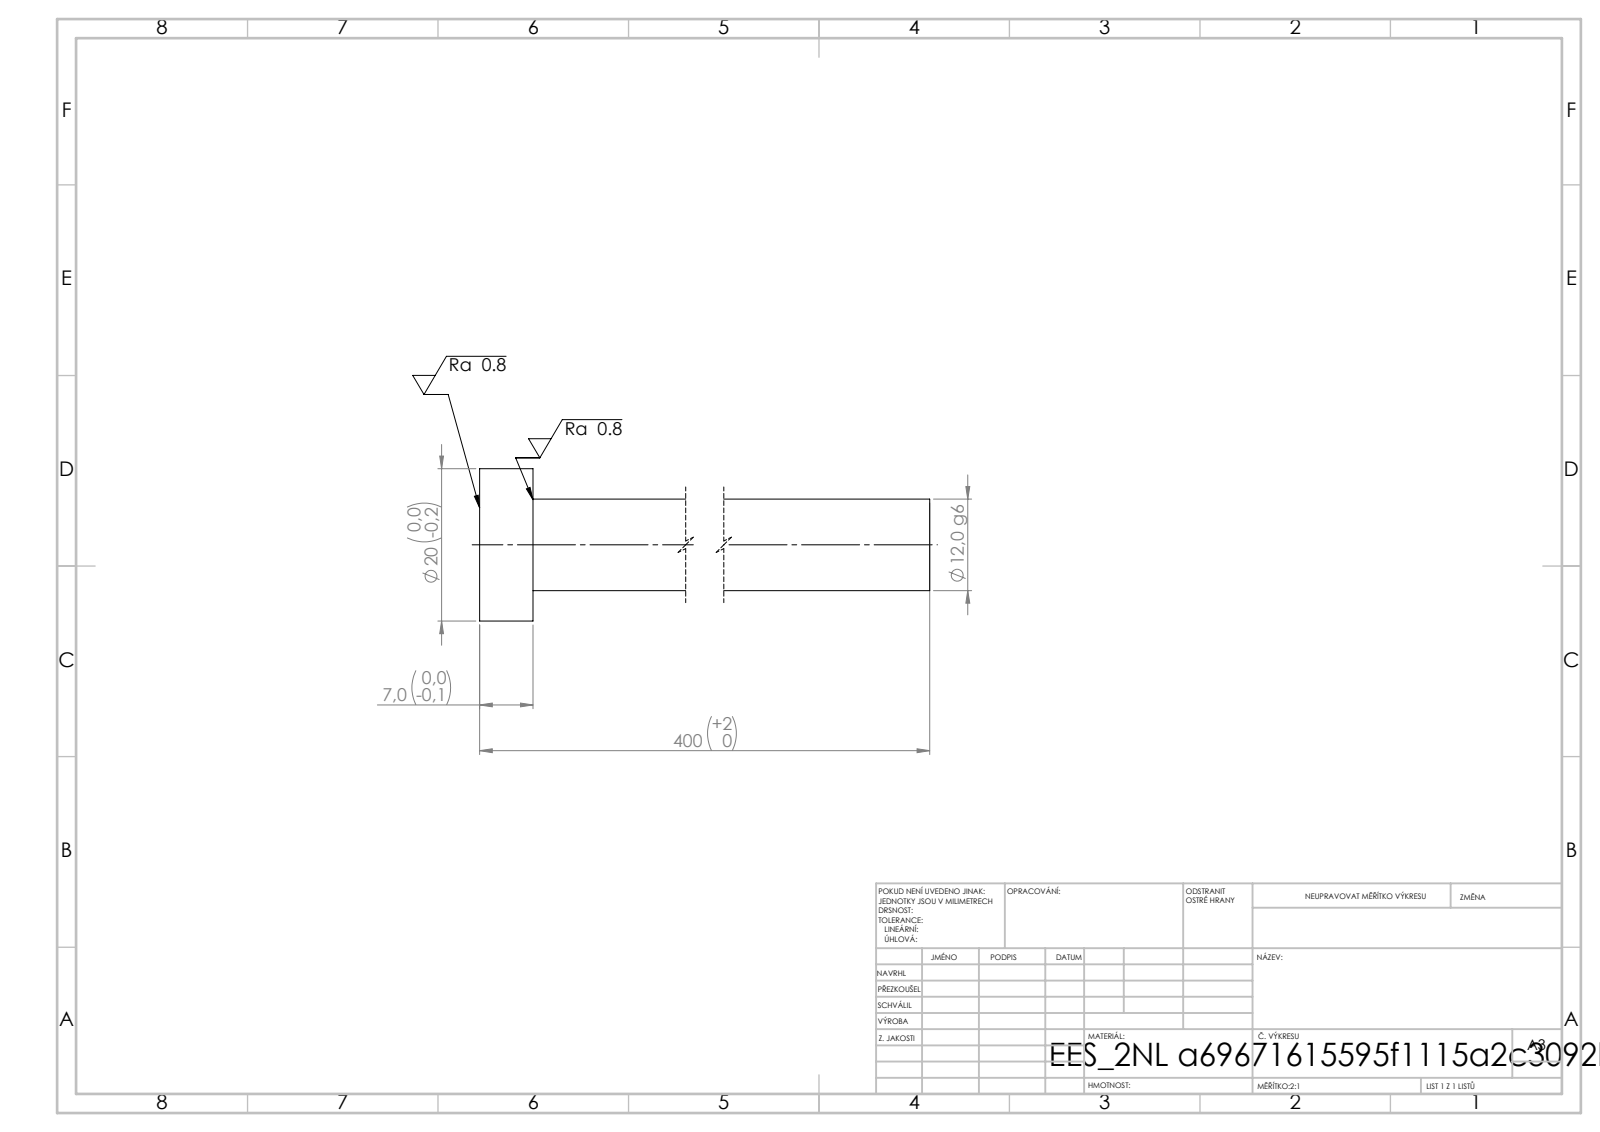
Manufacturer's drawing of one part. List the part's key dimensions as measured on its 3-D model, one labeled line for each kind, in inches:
STEP written by: SolidWorks 2019 (CONFIG_CONTROL_DESIGN)
Units: inches
Bodies: 1 solid, 7 faces (3 planar, 4 cylindrical, 0 other)
Overall size (bounding box): 15.748 × 0.787 × 0.787
Volume: 2.847 in³ · Surface area: 24.62 in²
Round bosses / shafts (diameter × count): ⌀0.787 ×1, ⌀0.472 ×1
Main face-to-face distances: 0.276, 15.748, 15.472
